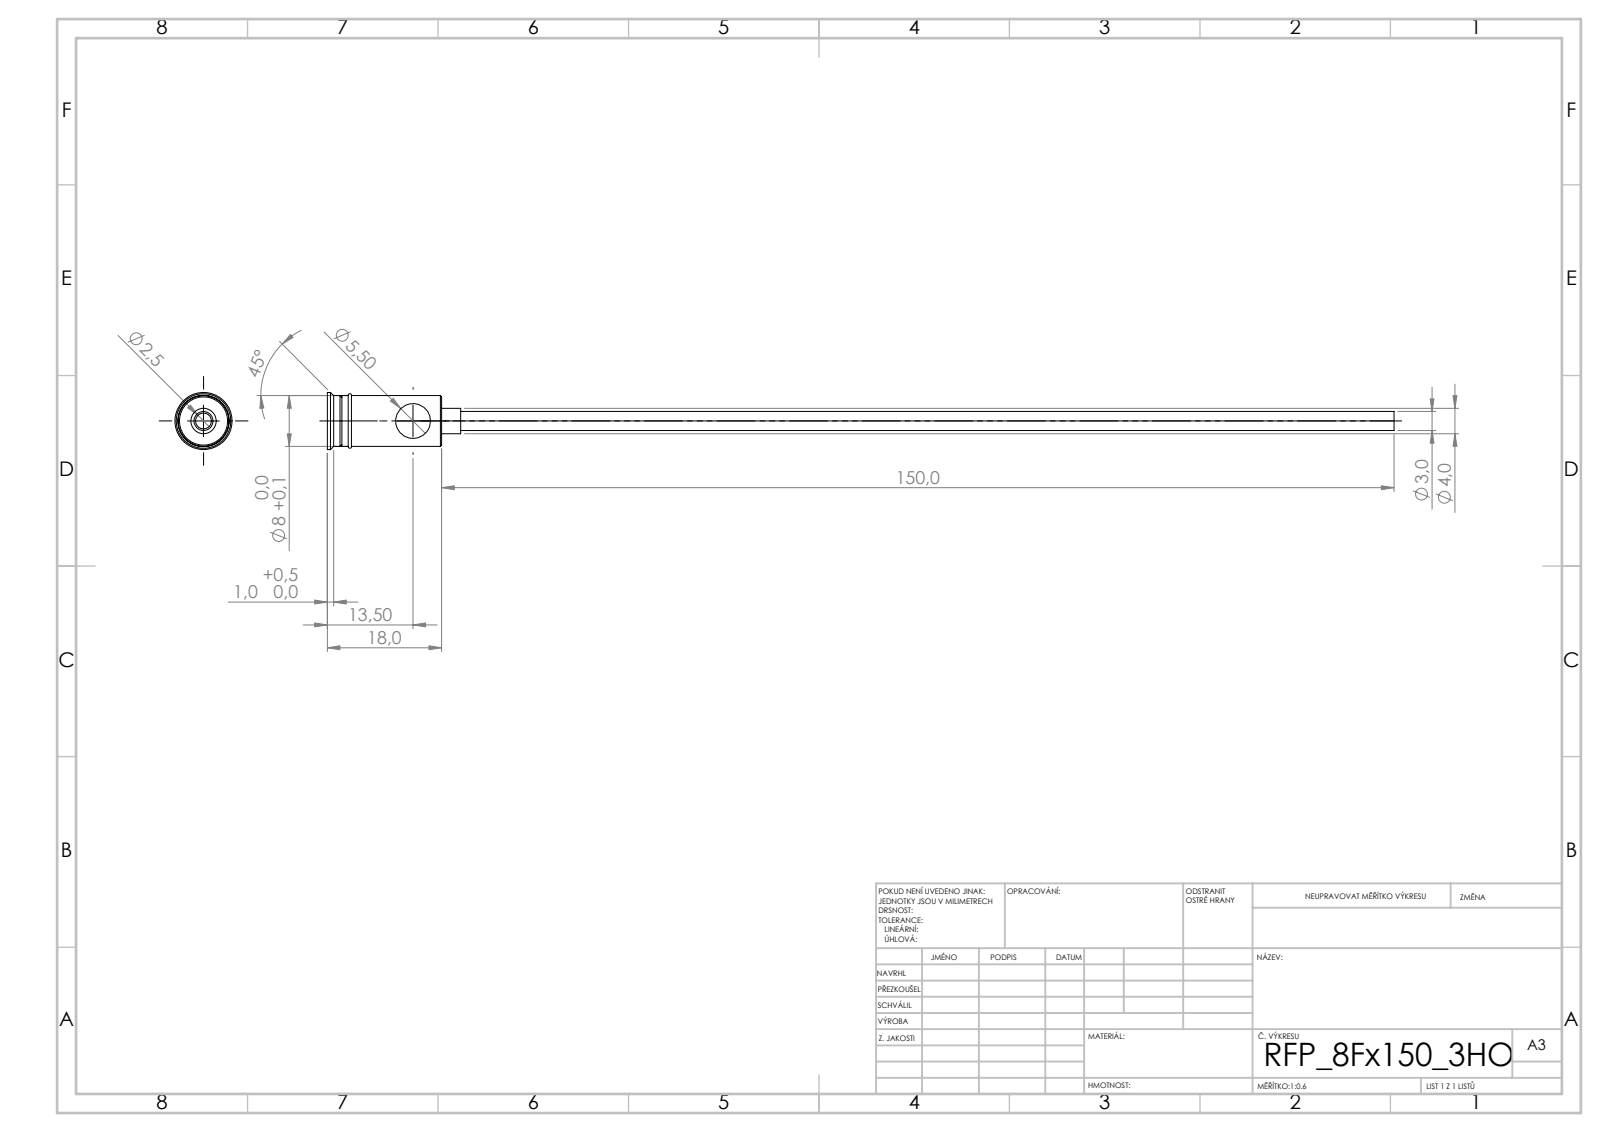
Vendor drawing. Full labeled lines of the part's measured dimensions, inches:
STEP written by: SolidWorks 2019 (CONFIG_CONTROL_DESIGN)
Units: inches
Bodies: 1 solid, 44 faces (20 planar, 16 cylindrical, 8 other)
Overall size (bounding box): 6.614 × 0.354 × 0.354
Volume: 0.064 in³ · Surface area: 5.098 in²
Round holes (diameter × count): ⌀0.098 ×1, ⌀0.217 ×1
Round bosses / shafts (diameter × count): ⌀0.354 ×1, ⌀0.315 ×1, ⌀0.157 ×1, ⌀0.118 ×1
Main face-to-face distances: 0.709, 0.134, 0.63, 0.079, 0.618, 0.091, 0.118, 0.736, 0.748, 0.827
